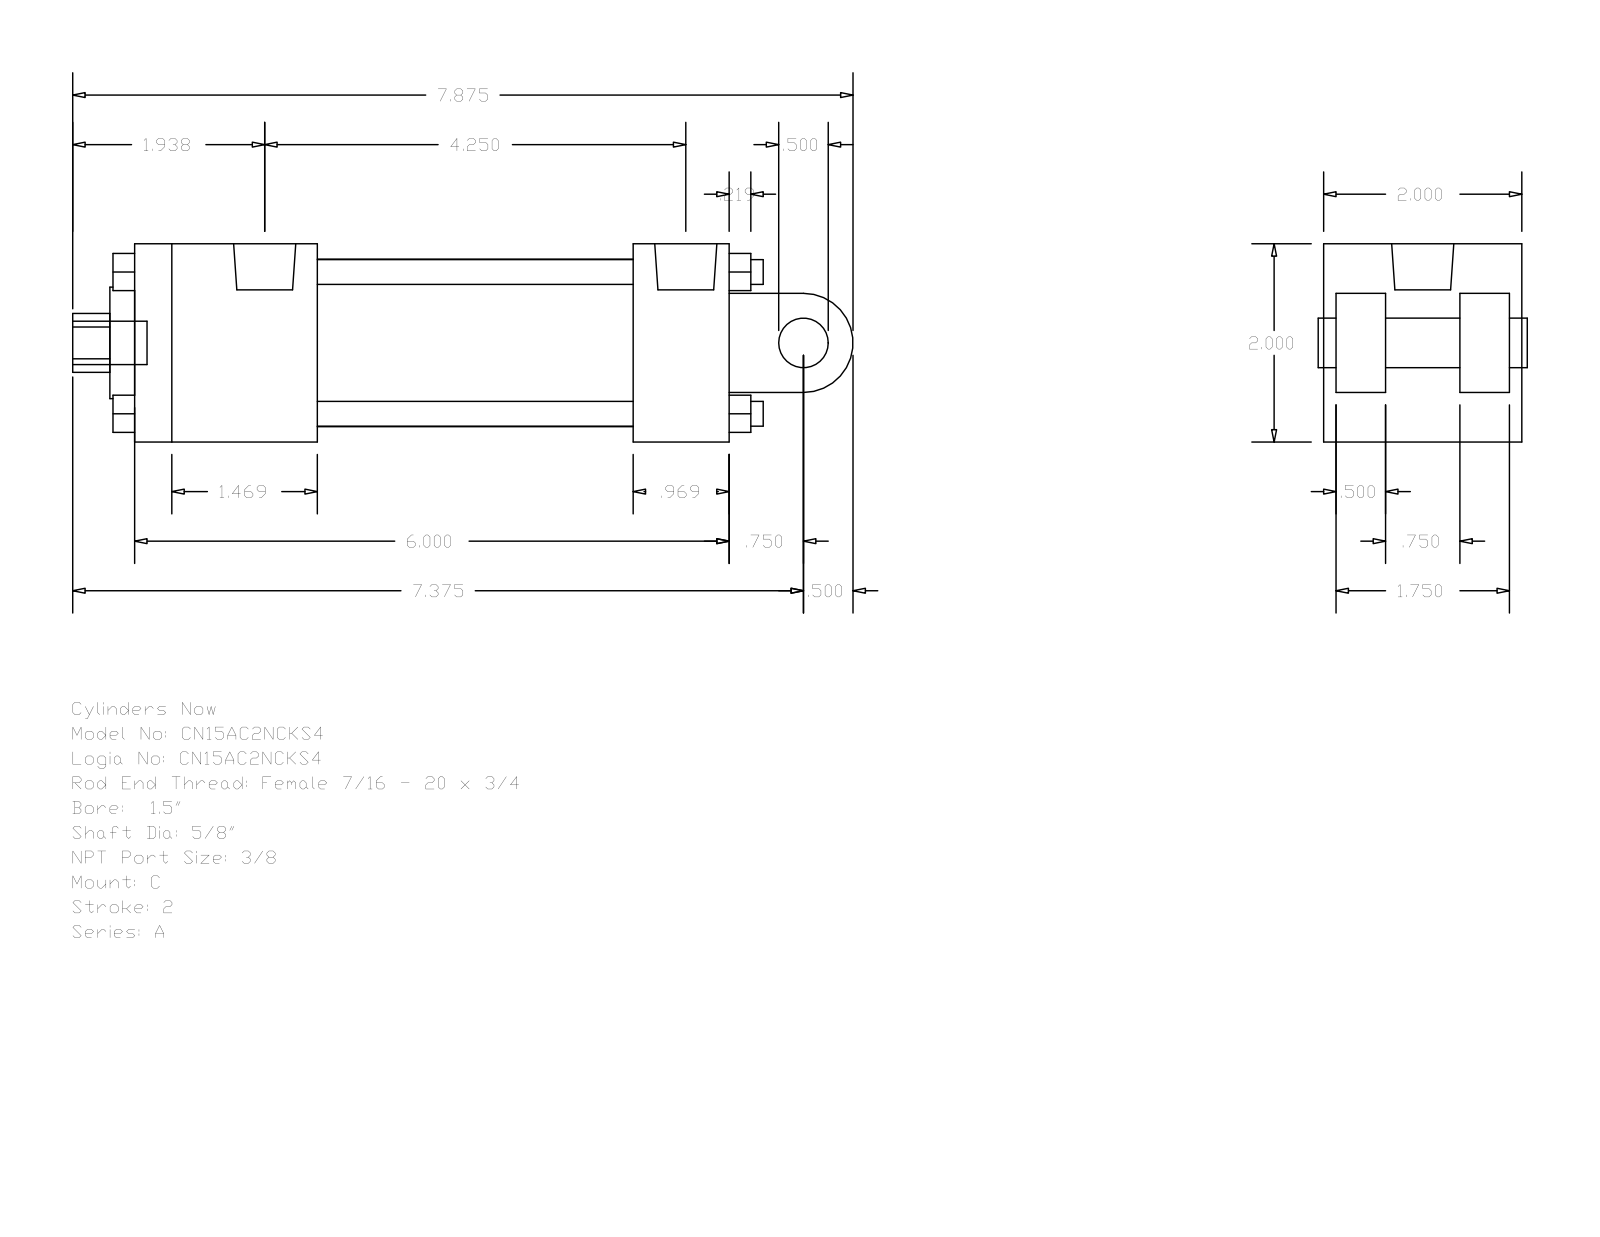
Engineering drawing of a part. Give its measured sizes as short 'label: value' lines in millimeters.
name: A_C__0150_0.625
written by: GSSL Pune (CONFIG_CONTROL_DESIGN)
unit: mm
bodies: 0 solids, 135 faces (102 planar, 33 cylindrical, 0 other)
size: 200.03 × 50.8 × 50.8
holes: 2× ⌀5.56, 1× ⌀15.88, 1× ⌀15.93, 1× ⌀28.57, 1× ⌀42.93
bosses: 4× ⌀6.35, 2× ⌀5.56, 1× ⌀15.93, 1× ⌀12.7, 1× ⌀11.11
rounds: 1× R7.54, 1× R12.7
face distances: 50.8, 12.7, 152.4, 3.17, 47.63, 15.87, 34.93, 31.76, 127.79, 24.61
hole spacings: 3.97
